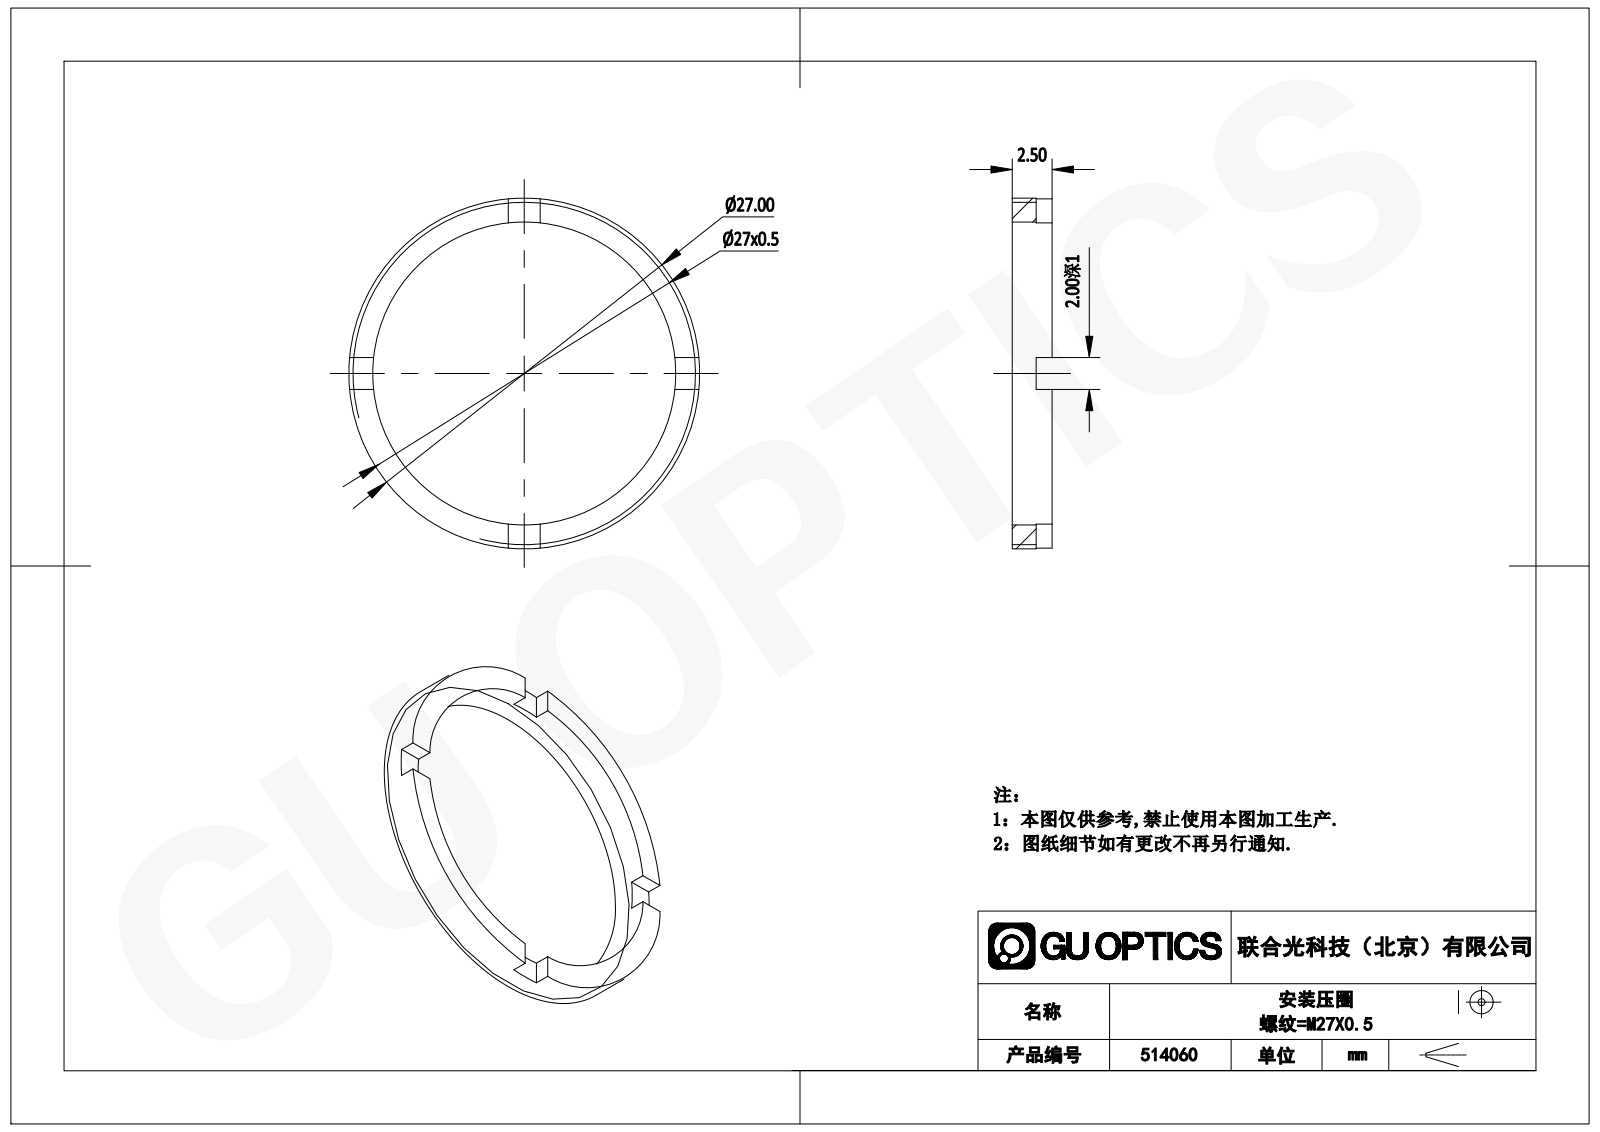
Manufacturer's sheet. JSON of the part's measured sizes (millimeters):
{"part_name": "514060", "step_written_by": "SolidWorks 2020 (CONFIG_CONTROL_DESIGN)", "units": "millimeters", "bodies": {"solids": 1, "faces": 21, "planar": 17, "cylindrical": 4, "other": 0}, "overall_size": [27, 27, 2.5], "volume_mm3": 288, "surface_area_mm2": 637, "round_holes": [[24, 1]], "round_bosses_or_shafts": [[27, 1]], "face_to_face_distances": [2.5, 1.5, 1, 2]}
